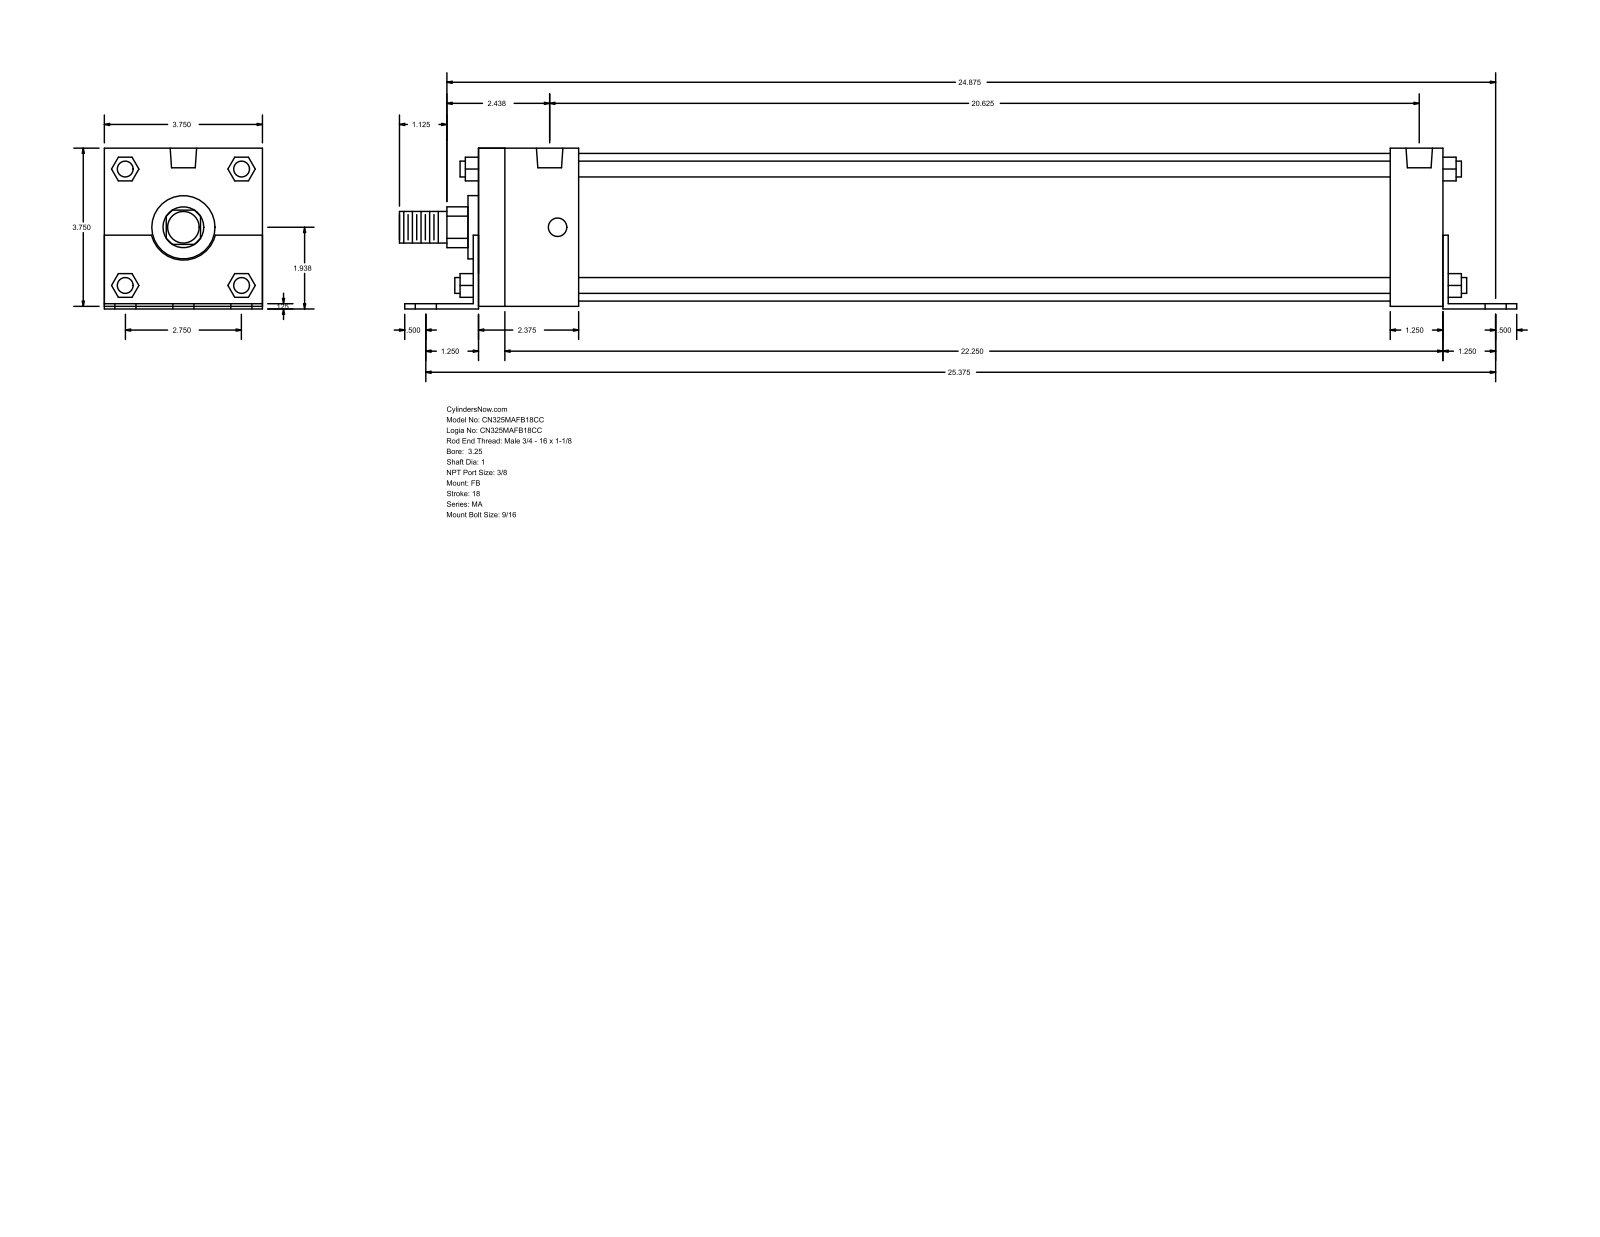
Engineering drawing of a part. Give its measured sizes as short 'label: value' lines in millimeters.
name: MA_FB__0325_1
written by: GSSL Pune (CONFIG_CONTROL_DESIGN)
unit: mm
bodies: 0 solids, 140 faces (105 planar, 35 cylindrical, 0 other)
size: 673.1 × 96.84 × 95.25
holes: 6× ⌀14.29, 4× ⌀11.11, 2× ⌀15.93
bosses: 4× ⌀9.53, 1× ⌀88.9, 1× ⌀38.1, 1× ⌀25.4, 1× ⌀19.05
rounds: 1× R12.29, 1× R19.81
face distances: 95.24, 3.17, 1.59, 96.83, 1.58, 93.66, 584.2, 581.03, 587.37, 552.45
hole spacings: 34.92, 645.48, 644.53, 57.78, 61.65, 69.84, 82.38, 86.71
